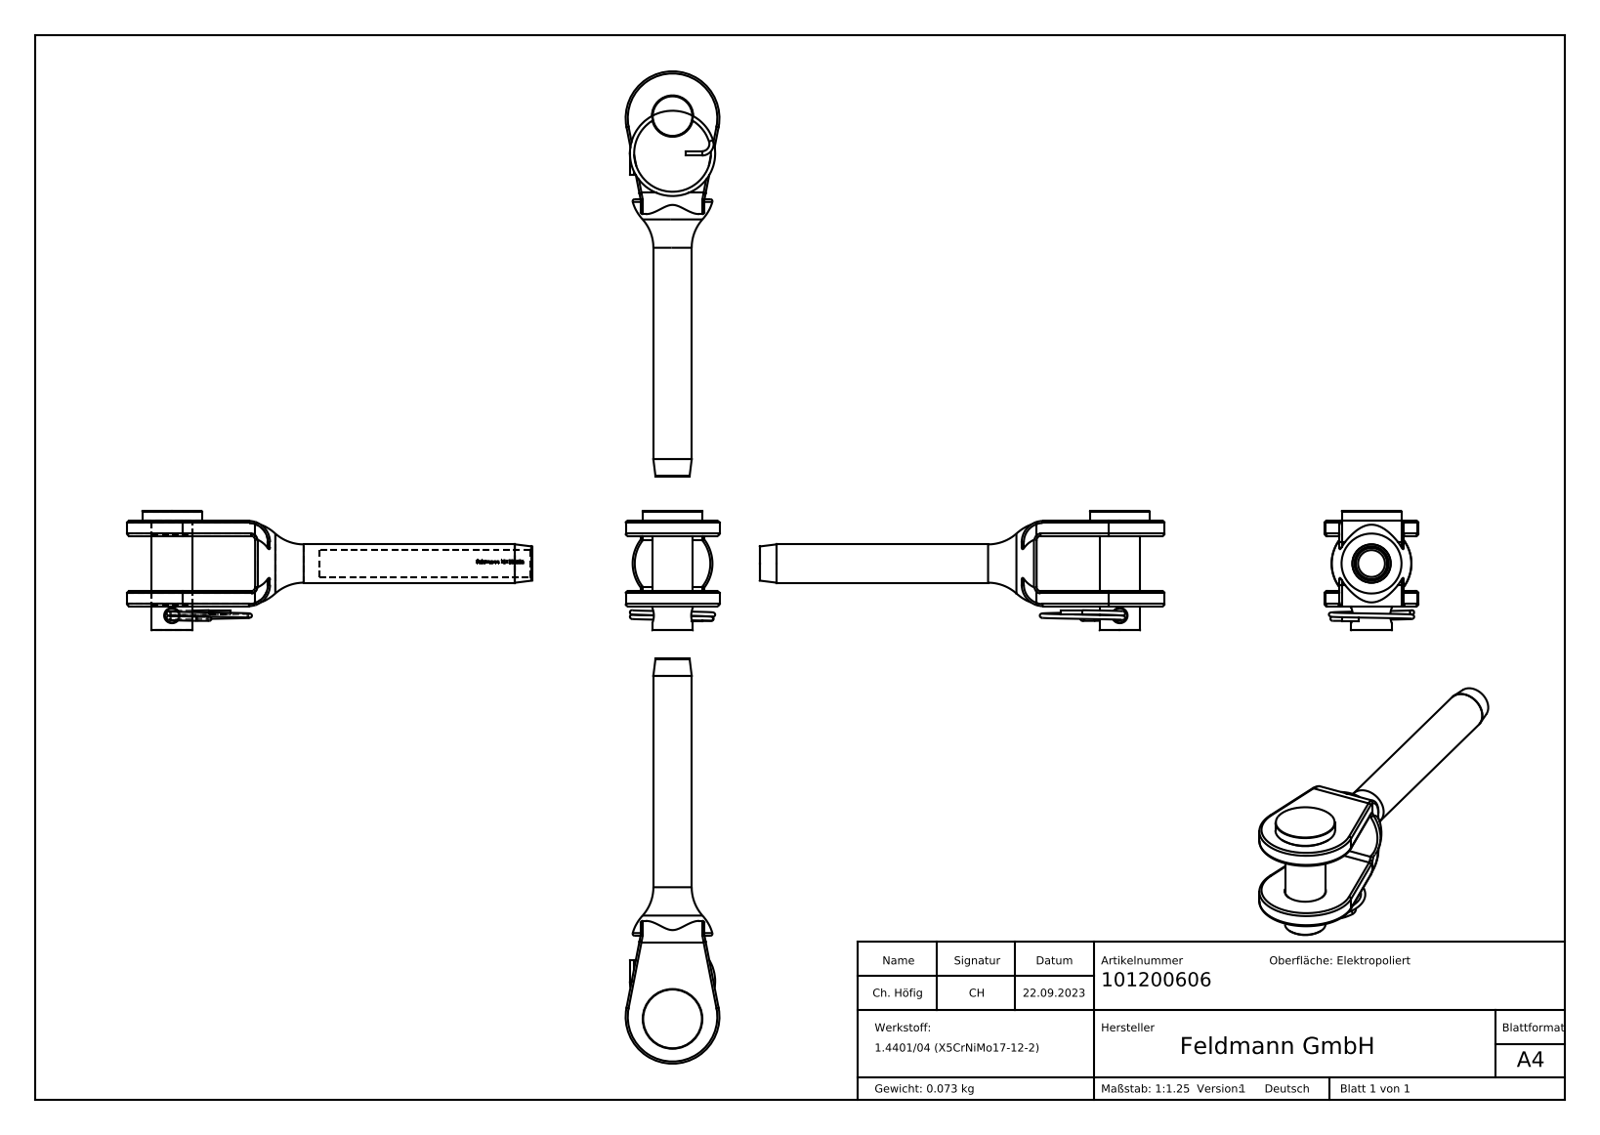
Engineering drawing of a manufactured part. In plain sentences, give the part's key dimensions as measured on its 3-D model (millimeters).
The part is named "101200X0X Teil1_101200606 Teil1; 101200606; 101200X0X Teil3_101200606 Teil3; 101200X0X Teil2_101200606 Teil2". Its 3-D file was written by "SolidWorks 2018 (CONFIG_CONTROL_DESIGN)". It is 3 solids with 309 faces: 102 planar, 59 cylindrical and 148 other. Overall it measures 95 by 28 by 22 millimeters. Its volume is 9 090 cubic millimeters and its surface area 7 458 square millimeters. Round holes: 1 of diameter 3.3, 1 of diameter 6.3, 1 of diameter 9.5. Round bosses or shafts: 2 of diameter 1, 1 of diameter 14, 1 of diameter 9. Partial cylindrical surfaces (rounded edges, fillets, slot ends): 10 of radius 0.5, 2 of radius 1, 2 of radius 5, 1 of radius 3.25, 1 of radius 11. The main face-to-face distances are 3.5, 16.5, 13, 20, 22.3, 18.8, 5.8, 2.3, 5.7, 9.2.
